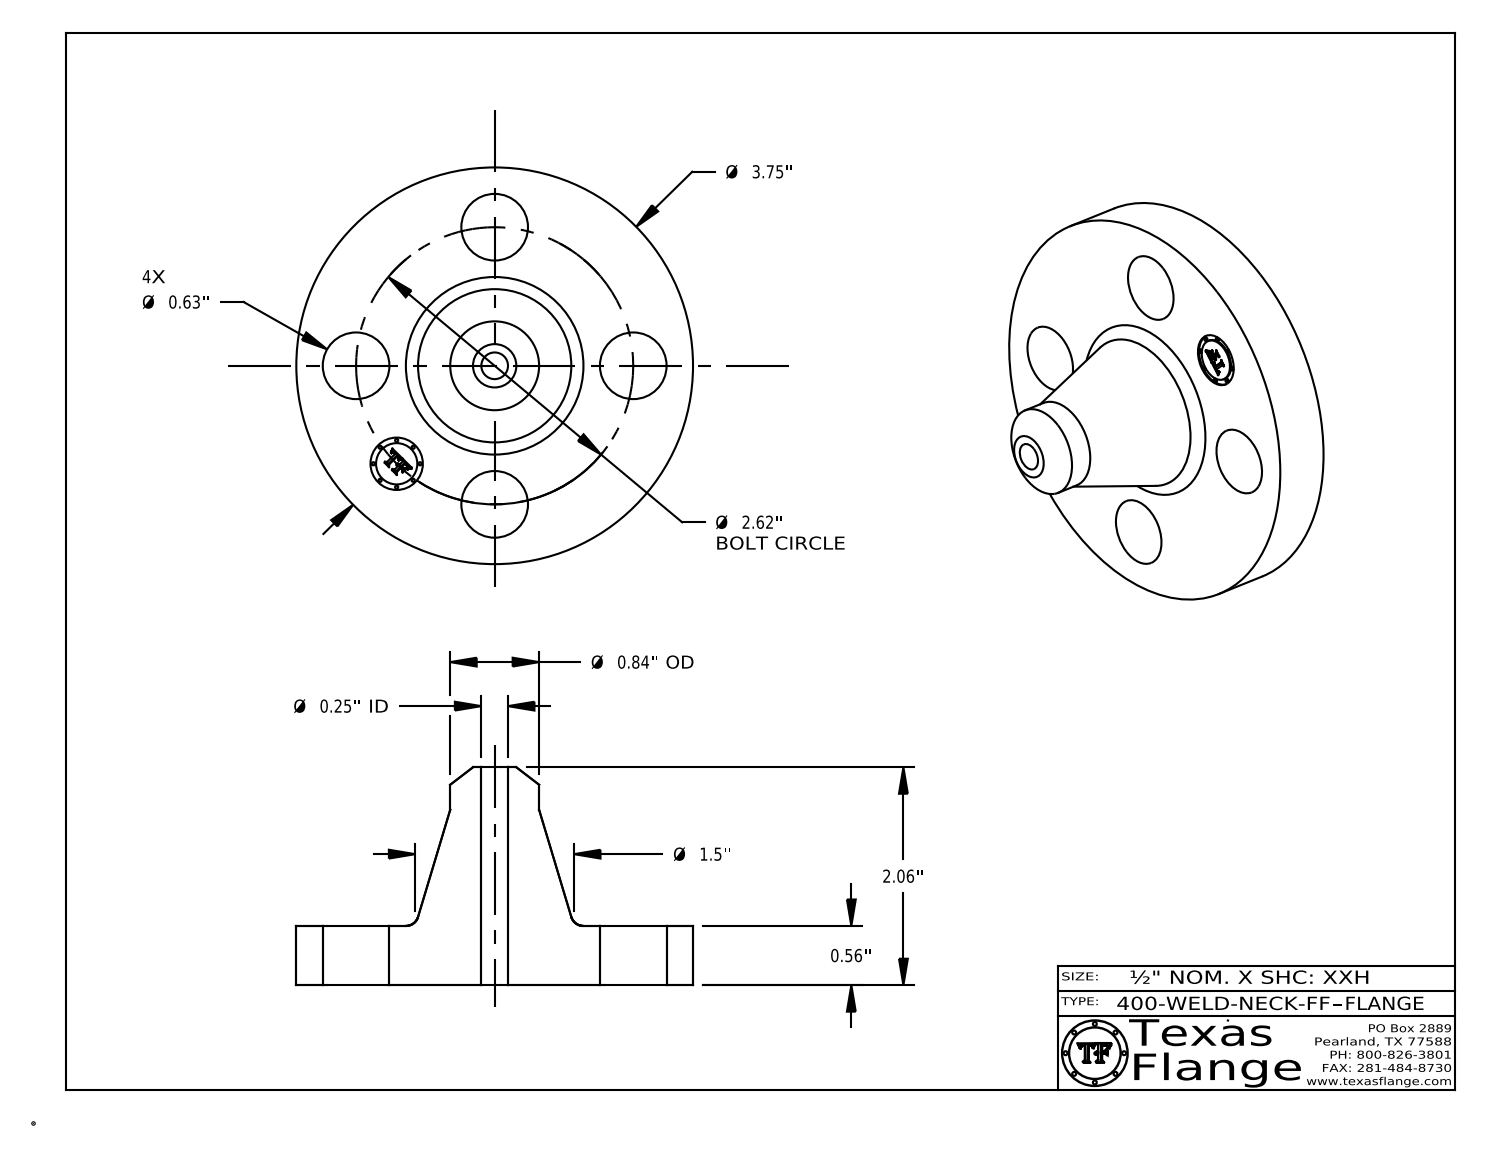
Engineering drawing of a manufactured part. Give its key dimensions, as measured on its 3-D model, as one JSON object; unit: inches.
{"part_name": "400-WELD-NECK-FF", "step_written_by": "CATIA V5 STEP AP214 (AUTOMOTIVE_DESIGN)", "units": "inches", "bodies": {"solids": 1, "faces": 408, "planar": 368, "cylindrical": 34, "other": 6}, "overall_size": [3.75, 3.75, 2.06], "volume_in3": 6.786, "surface_area_in2": 35.87, "round_holes": [[0.63, 4], [0.252, 1], [0.495, 1]], "round_bosses_or_shafts": [[0.03, 8], [3.75, 1], [0.84, 1], [0.39, 1]], "face_to_face_distances": [0.56, 2.06, 1.5, 0.545, 0.015, 1.515, 0.148, 0.144, 0.027, 0.096], "hole_center_spacings": [1.31, 1.852, 1.003, 2.42, 2.62, 1.31]}
